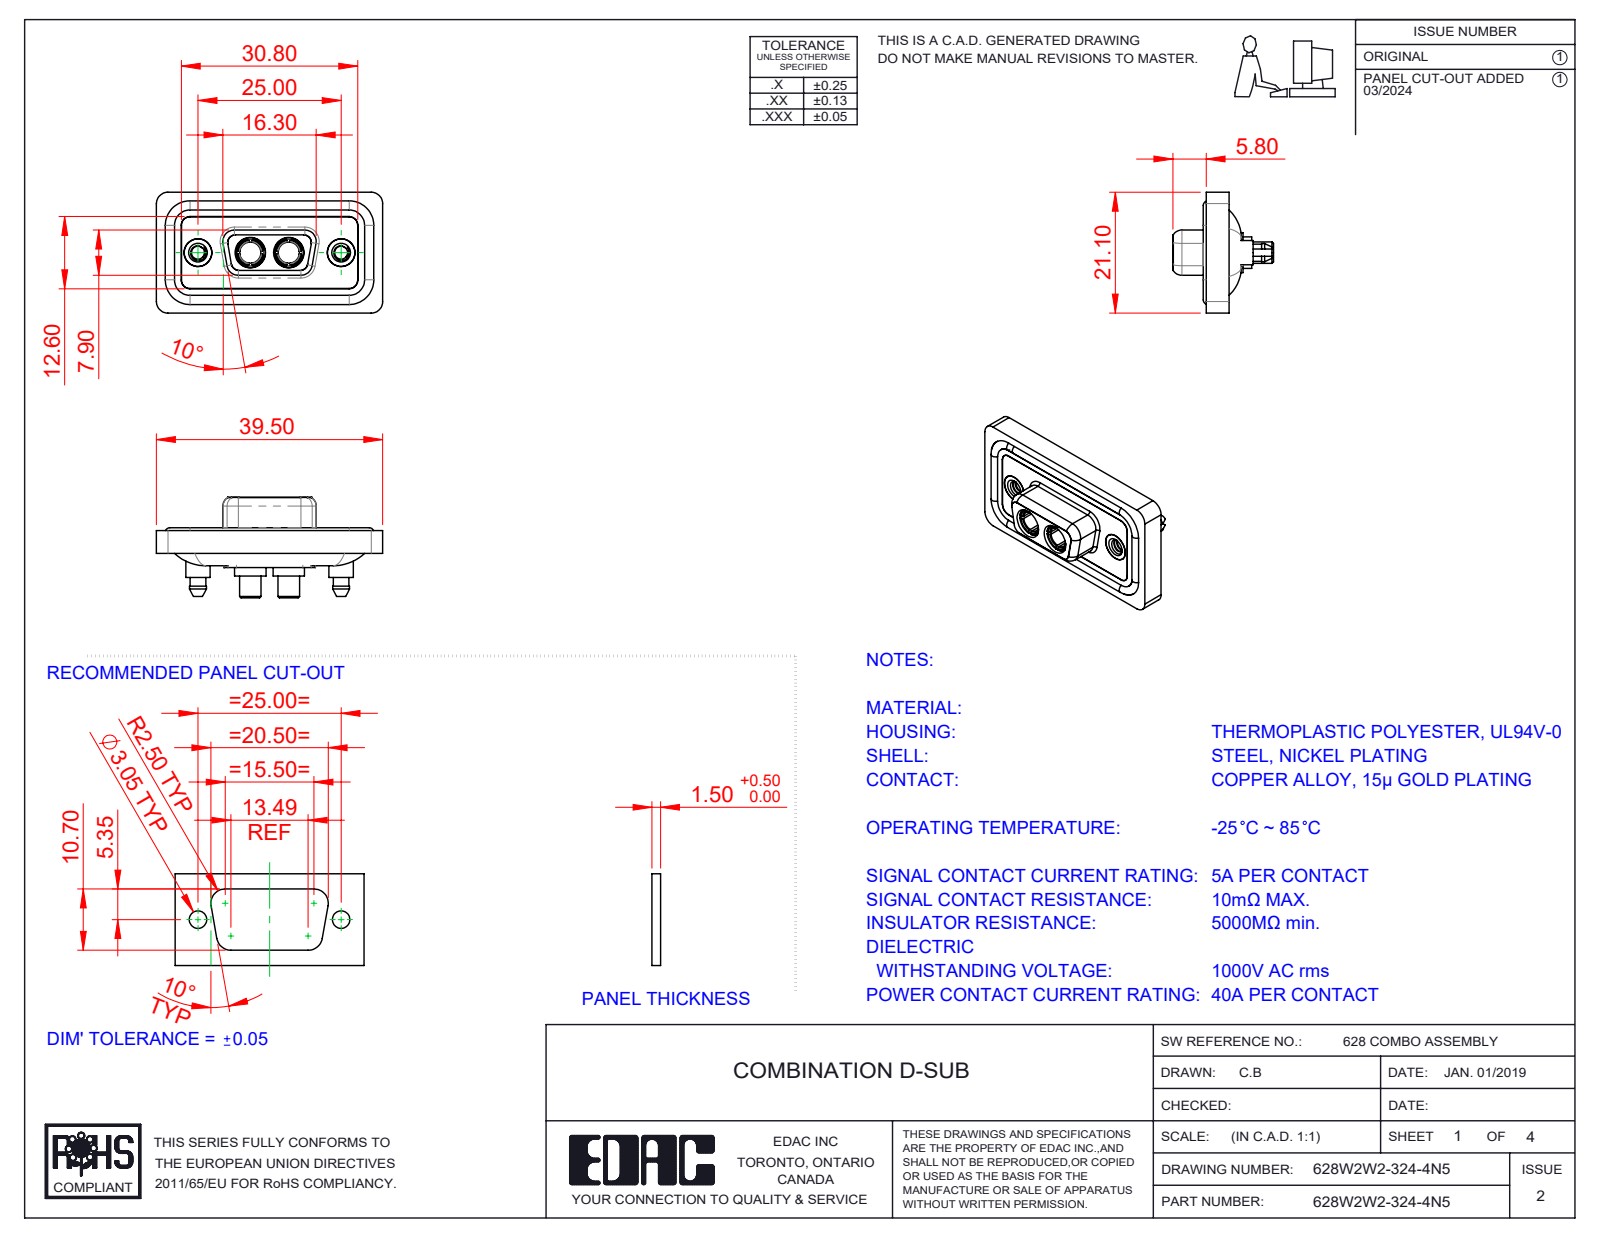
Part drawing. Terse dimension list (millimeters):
name: 628Combo Waterproof Housing_09 Contacts; 628W2W2-324-4N5; 628Combo Shell Rear_09 Contacts; 628Combo Shell Front_09 Contacts (+3 more)
written by: SolidWorks 2023 (CONFIG_CONTROL_DESIGN)
unit: mm
bodies: 11 solids, 584 faces (179 planar, 266 cylindrical, 139 other)
size: 39.5 × 21.1 × 17.55
volume: 4 883 mm³; area: 7 991 mm²
holes: 4× ⌀4.85, 2× ⌀2.26, 2× ⌀3.7, 2× ⌀4, 2× ⌀4.05, 2× ⌀5, 2× ⌀5.3
bosses: 4× ⌀1.6, 2× ⌀5.5, 2× ⌀5.4, 2× ⌀5.2, 2× ⌀4.96, 2× ⌀4.95, 2× ⌀4.8, 2× ⌀4.75
rounds: 24× R1.5, 18× R2, 10× R1.6, 8× R1.35, 4× R0.25, 4× R0.5, 4× R0.6, 4× R0.65
face distances: 0.4, 1.8, 1.1, 2.9, 1.6, 0.5, 5.65, 7.45, 4, 1.5
hole spacings: 9.14, 15.86, 6.72, 25
